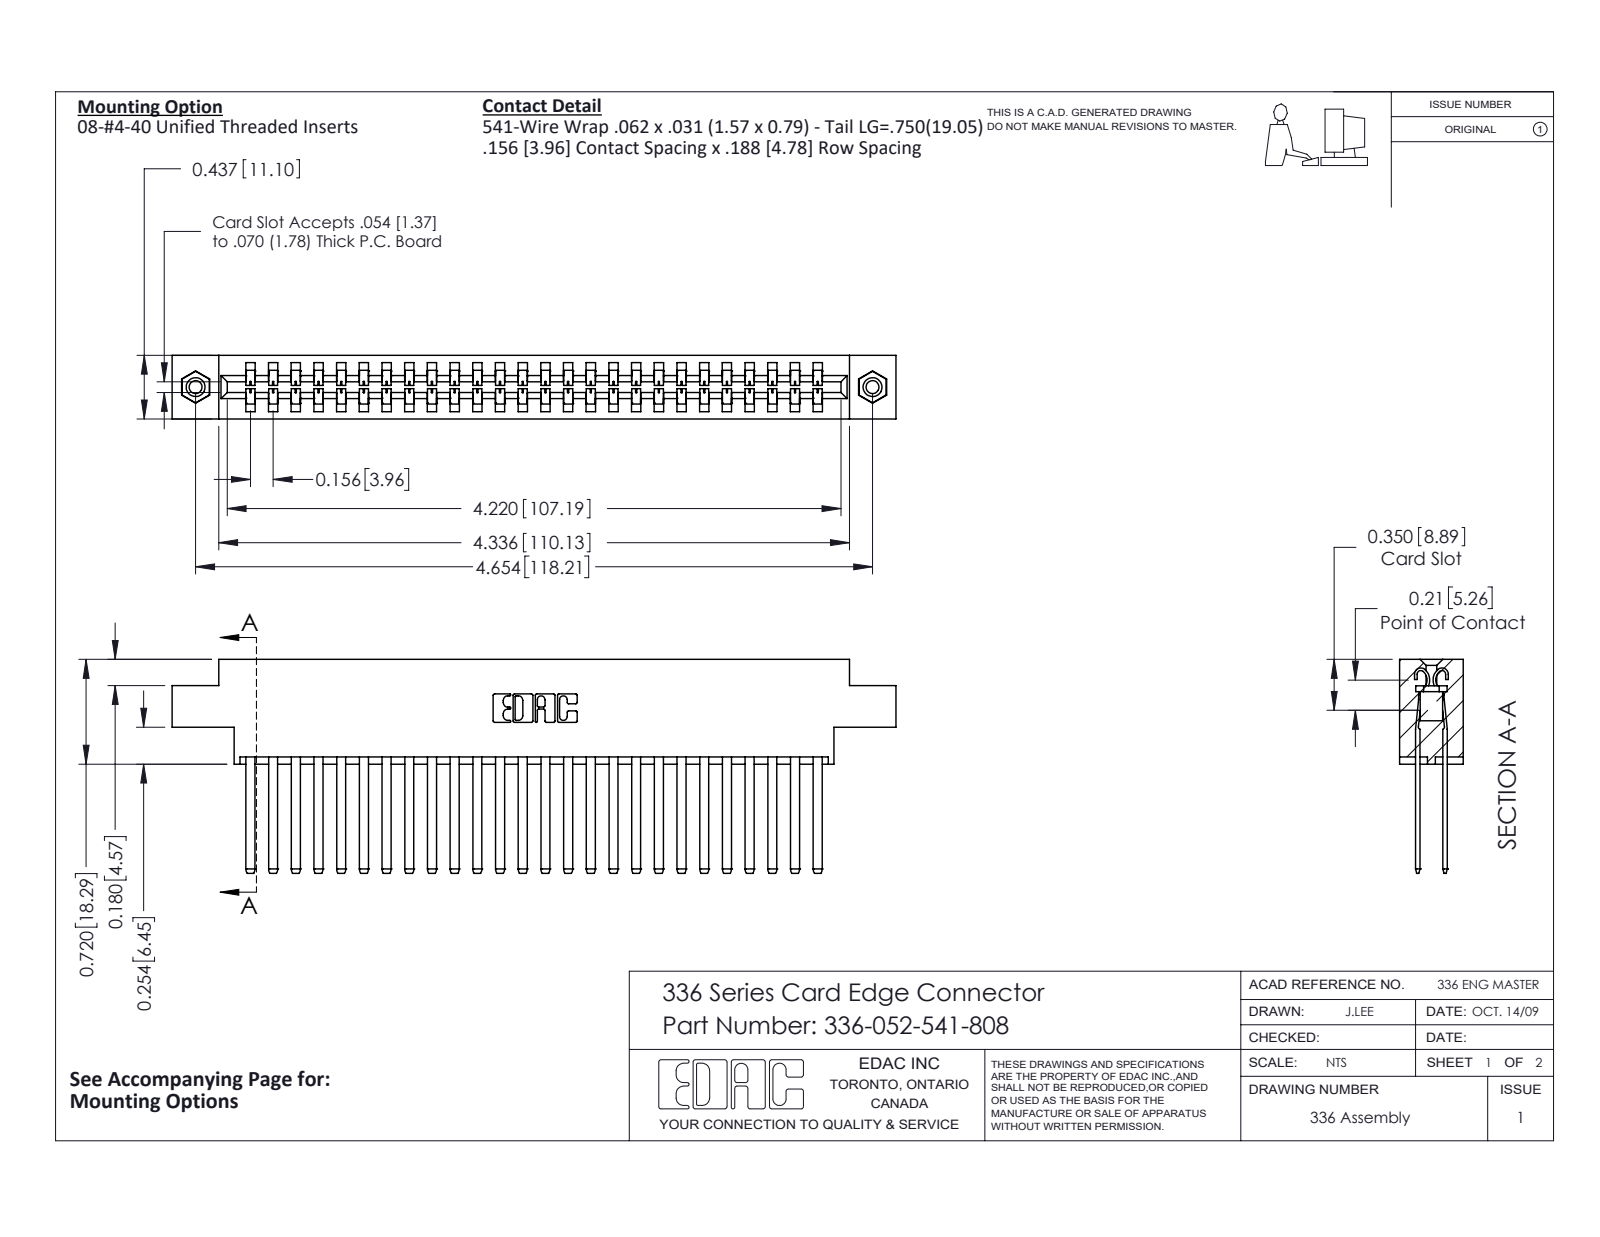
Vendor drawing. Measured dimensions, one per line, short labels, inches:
name: 345-250-001_345-250-003-102; 336-290-001_336-290-541; 336 Part_Offset - .156 Dia - TI; 336-052-541-808
written by: SolidWorks 2020 (CONFIG_CONTROL_DESIGN)
unit: in
bodies: 55 solids, 2362 faces (1458 planar, 888 cylindrical, 16 other)
size: 4.977 × 1.47 × 0.437
volume: 1.16 in³; area: 37.35 in²
holes: 2× ⌀0.089, 2× ⌀0.125, 2× ⌀0.156
bosses: 2× ⌀0.155
rounds: 104× R0.004, 52× R0.056, 22× R0.01, 6× R0.007, 6× R0.031, 4× R0.022, 4× R0.04, 3× R0.026
face distances: 0.188, 0.328, 0.14, 0.297, 0.109, 0.031, 0.437, 0.033, 0.181, 0.146
hole spacings: 4.654
